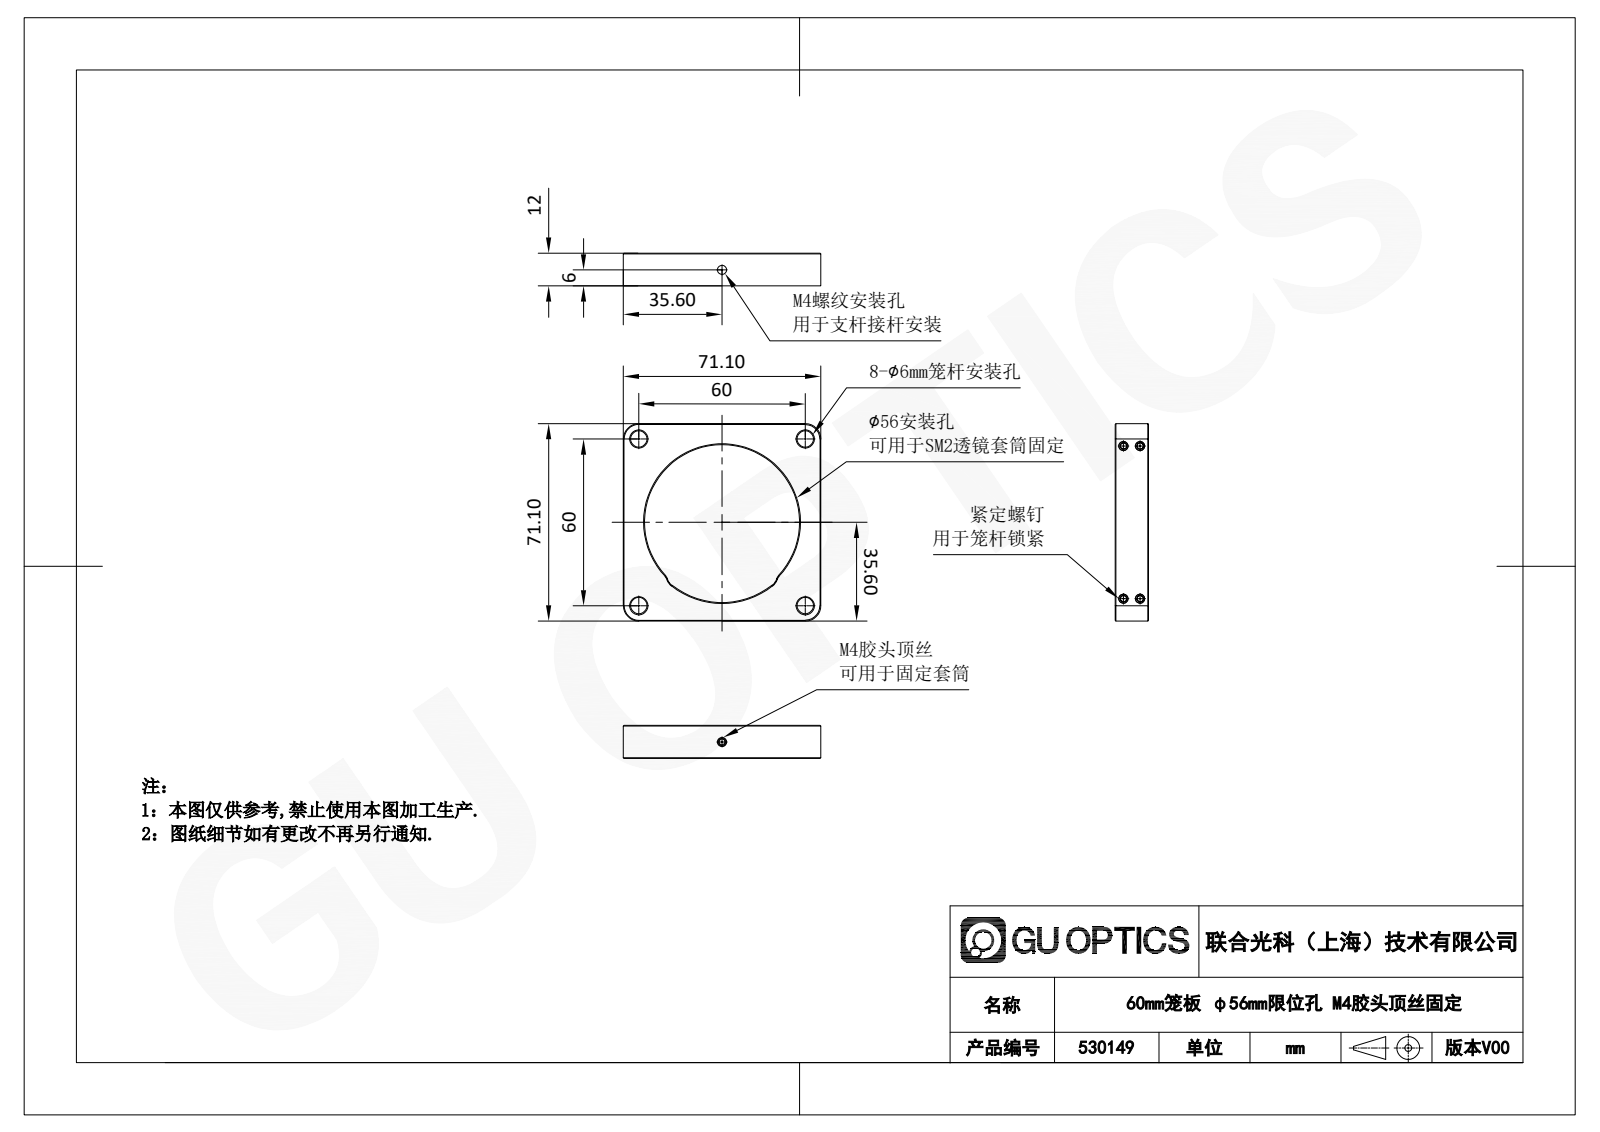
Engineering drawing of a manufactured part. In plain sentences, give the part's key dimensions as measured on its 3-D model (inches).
The part is named "530149". Its 3-D file was written by "SolidWorks 2020 (CONFIG_CONTROL_DESIGN)". It is 10 solids with 233 faces: 96 planar, 34 cylindrical and 103 other. Overall it measures 2.799 by 2.799 by 0.472 inches. Its volume is 1.753 cubic inches and its surface area 18.2 square inches. Round holes: 4 of diameter 0.098, 4 of diameter 0.236, 1 of diameter 0.13. Round bosses or shafts: 5 of diameter 0.118, 1 of diameter 0.157. Partial cylindrical surfaces (rounded edges, fillets, slot ends): 4 of radius 0.219, 2 of radius 0.118, 2 of radius 0.197, 1 of radius 1.102, 1 of radius 1.142. The main face-to-face distances are 0.472, 2.799, 2.299, 0.059, 0.079, 2.563, 0.236, 2.72, 0.234, 0.281. The hole center spacings are 2.362, 0.236, 2.165, 2.178, 3.341.
